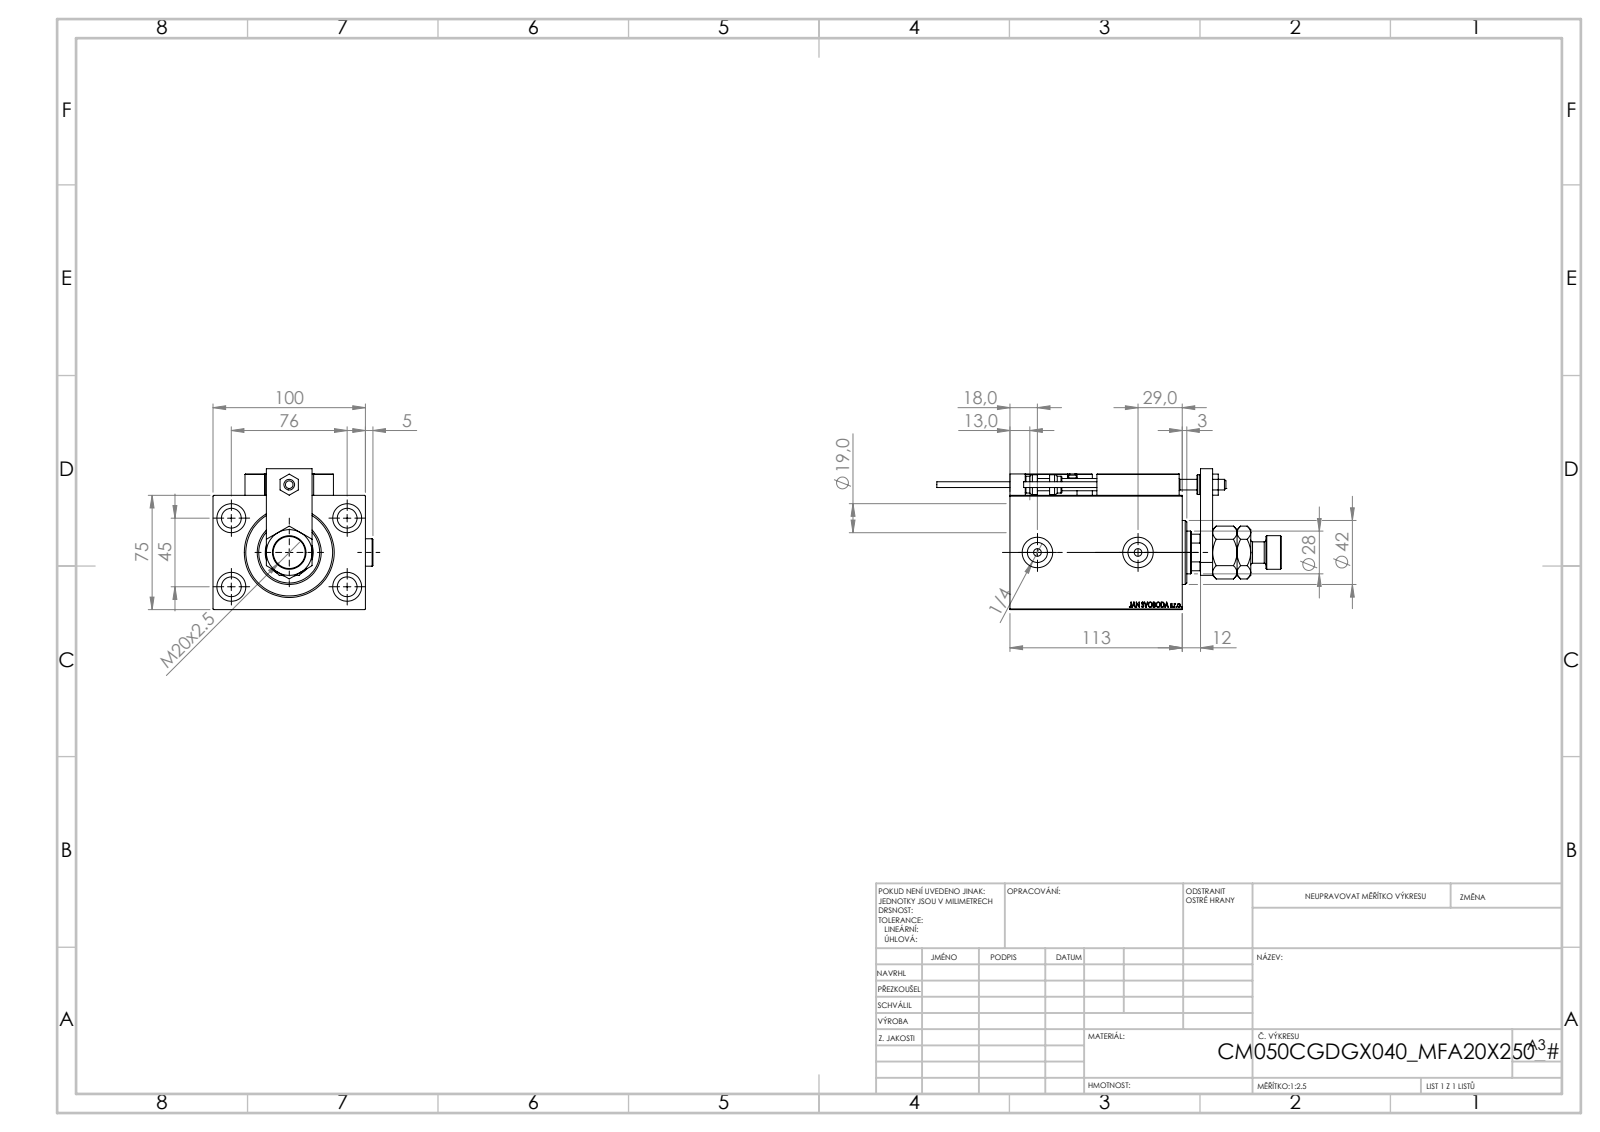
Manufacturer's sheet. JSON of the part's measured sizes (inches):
{"part_name": "X_Y_MFA; ALLEN BOLT D8; ALLEN BOLT D5; SWITCH X (+7 more)", "step_written_by": "SolidWorks 2019 (CONFIG_CONTROL_DESIGN)", "units": "inches", "bodies": {"solids": 24, "faces": 1351, "planar": 581, "cylindrical": 204, "other": 566}, "overall_size": [8.898, 3.937, 3.642], "volume_in3": 48.27, "surface_area_in2": 219.6, "round_holes": [[0.315, 5], [0.126, 4], [0.157, 4], [0.197, 4], [0.512, 4], [0.748, 4], [0.787, 3], [0.518, 2], [0.276, 1], [0.728, 1], [1.102, 1], [1.24, 1]], "round_bosses_or_shafts": [[0.197, 2], [0.15, 2], [1.654, 1], [0.866, 1], [0.551, 1], [0.512, 1], [0.433, 1]], "partial_cylinders_radius": [[0.012, 30], [0.118, 2], [0.531, 1]], "face_to_face_distances": [2.953, 3.937, 4.449, 0.551, 2.687, 1.762, 0.315, 0.787, 1.181, 0.394], "hole_center_spacings": [1.739, 0.448, 0.787, 1.165, 1.169, 1.42, 1.661, 1.729]}
